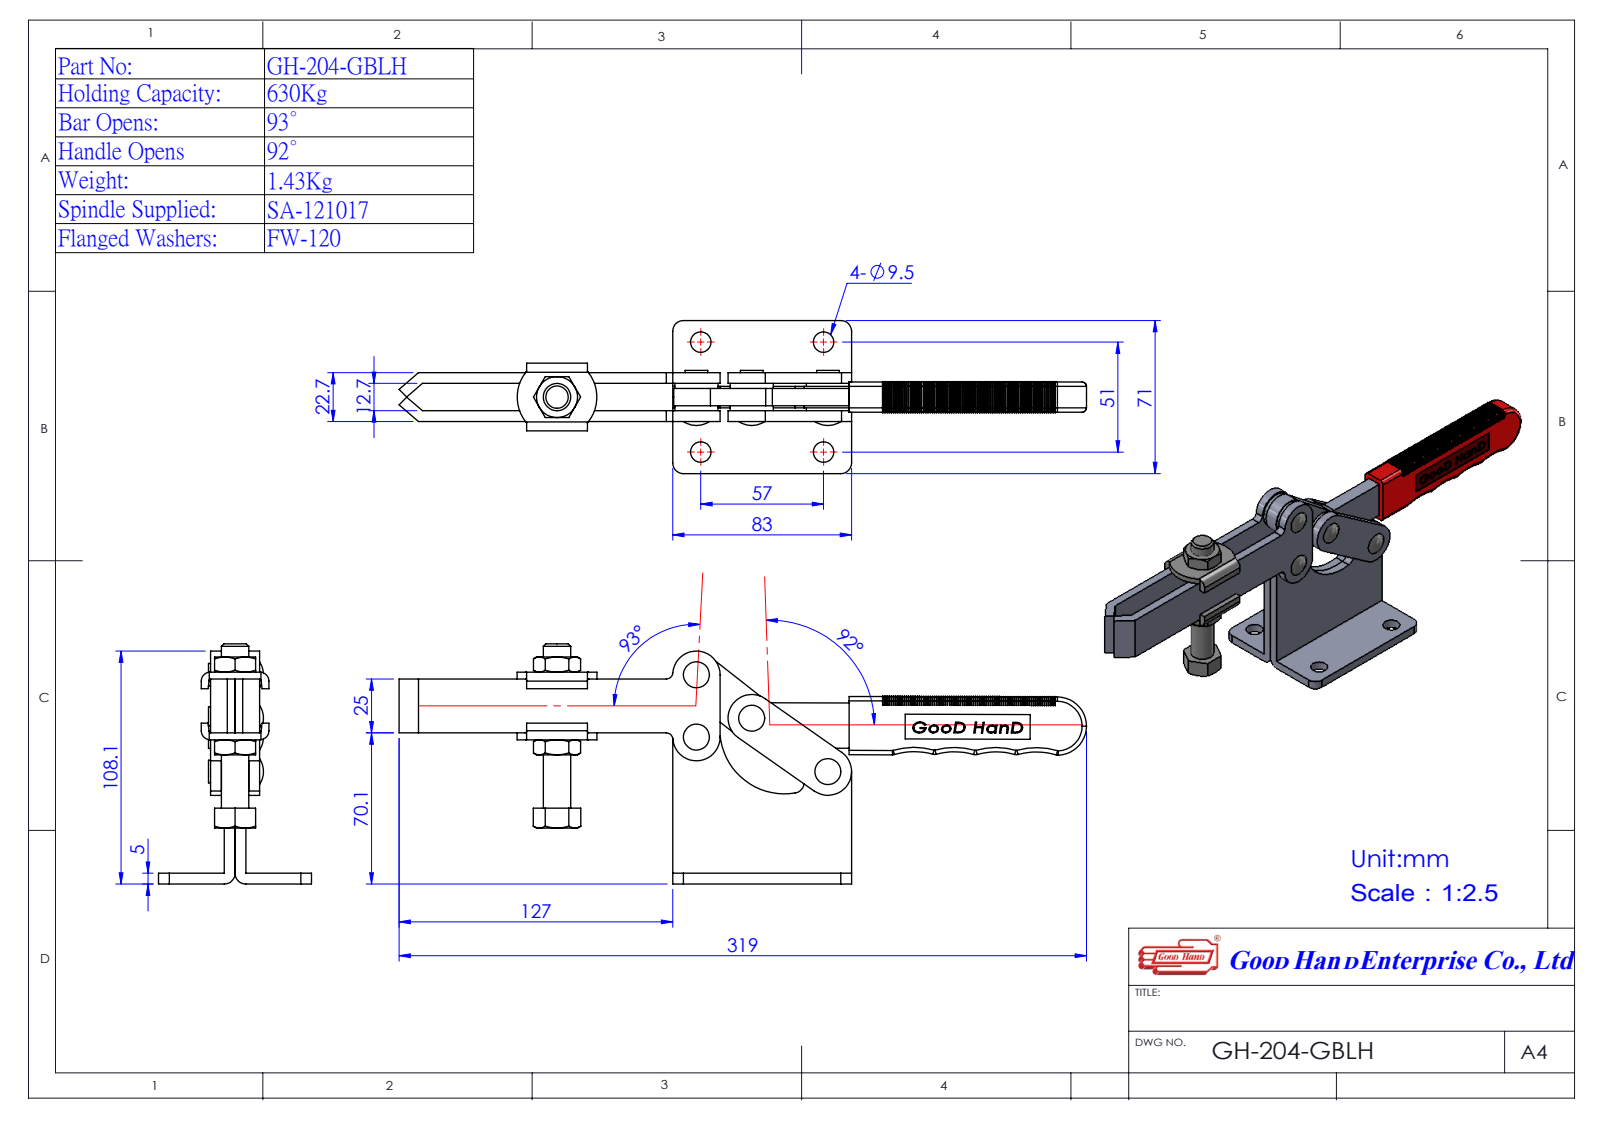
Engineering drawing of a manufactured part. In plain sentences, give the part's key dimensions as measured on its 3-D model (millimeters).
The part is named "Group1^GH-204-GBLH(簡化)-1; Group2^GH-204-GBLH(簡化)-1; Group1^組合件8; Group5^GH-204-G(簡化) (+2 more)". Its 3-D file was written by "SolidWorks 2016 (AUTOMOTIVE_DESIGN)". It is 5 solids with 262 faces: 108 planar, 112 cylindrical and 42 other. Overall it measures 319 by 128.35 by 71 millimeters. Its volume is 212 558 cubic millimeters and its surface area 78 292 square millimeters. Round holes: 4 of diameter 8, 4 of diameter 9.5. Round bosses or shafts: 4 of diameter 20, 4 of diameter 10.5, 2 of diameter 22, 1 of diameter 12.7. Partial cylindrical surfaces (rounded edges, fillets, slot ends): 7 of radius 3, 7 of radius 5, 4 of radius 1, 4 of radius 4.2, 4 of radius 32, 2 of radius 11, 1 of radius 10.5, 1 of radius 13.5. The main face-to-face distances are 5, 16.35, 6.35, 17.7, 1.35, 11.35, 4.35, 18.35, 0.65, 2. The hole center spacings are 51, 57, 76.49, 27.12, 28.9, 32.63, 43.14, 63.06.
